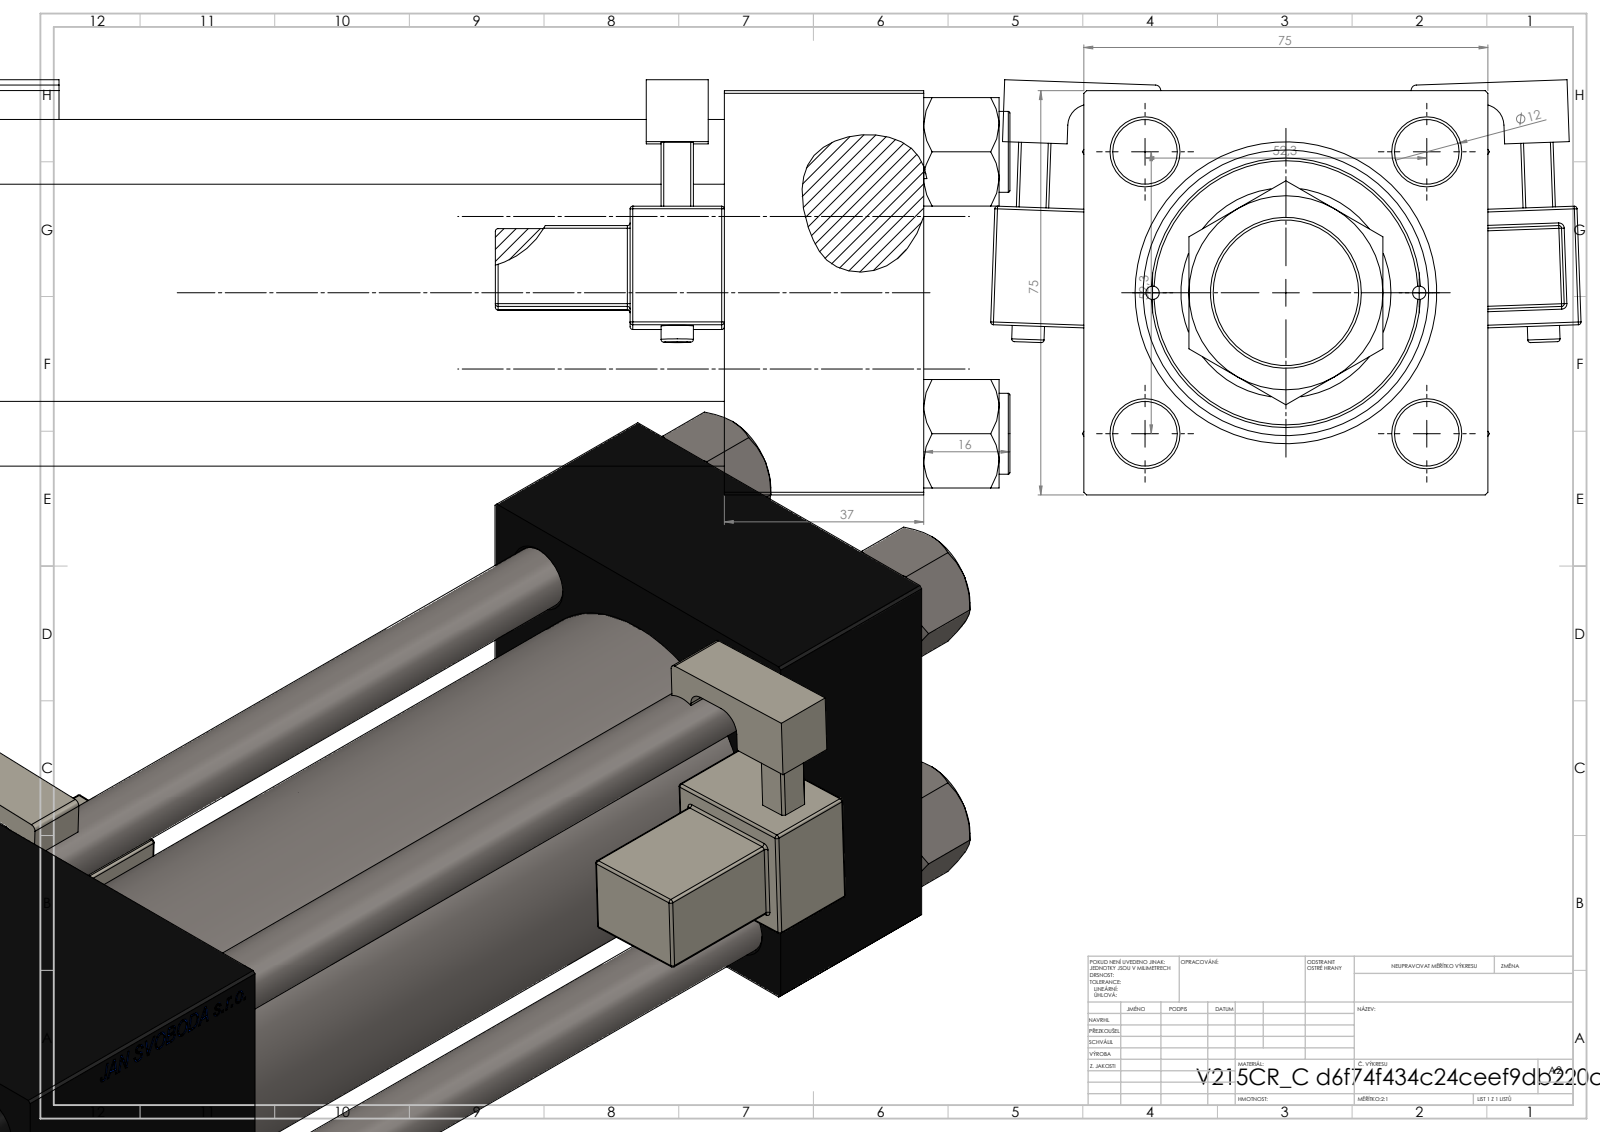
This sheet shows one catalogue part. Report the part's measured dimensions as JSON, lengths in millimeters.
{"part_name": "NUT_M5_C; MFA; V215CR_C_TYCINKA; V215CR_MSU (+3 more)", "step_written_by": "SolidWorks 2019 (CONFIG_CONTROL_DESIGN)", "units": "millimeters", "bodies": {"solids": 14, "faces": 1360, "planar": 602, "cylindrical": 154, "other": 604}, "overall_size": [334, 109.57, 77.03], "volume_mm3": 933392, "surface_area_mm2": 224421, "round_holes": [[12, 4], [2.5, 2], [7, 2], [20.96, 2], [30, 2], [25.5, 1], [36, 1], [39, 1], [41, 1], [53, 1]], "round_bosses_or_shafts": [[15, 4], [6, 2], [56, 1], [50, 1], [28, 1], [18, 1]], "partial_cylinders_radius": [[0.5, 48], [1, 2], [2.5, 2], [4, 2], [17.5, 1]], "face_to_face_distances": [75, 37, 59, 175, 138, 234, 197, 25, 84, 205.3], "hole_center_spacings": [26.19, 36.98, 52.3, 57.22, 24.75, 73.96, 49.5, 173.5]}
